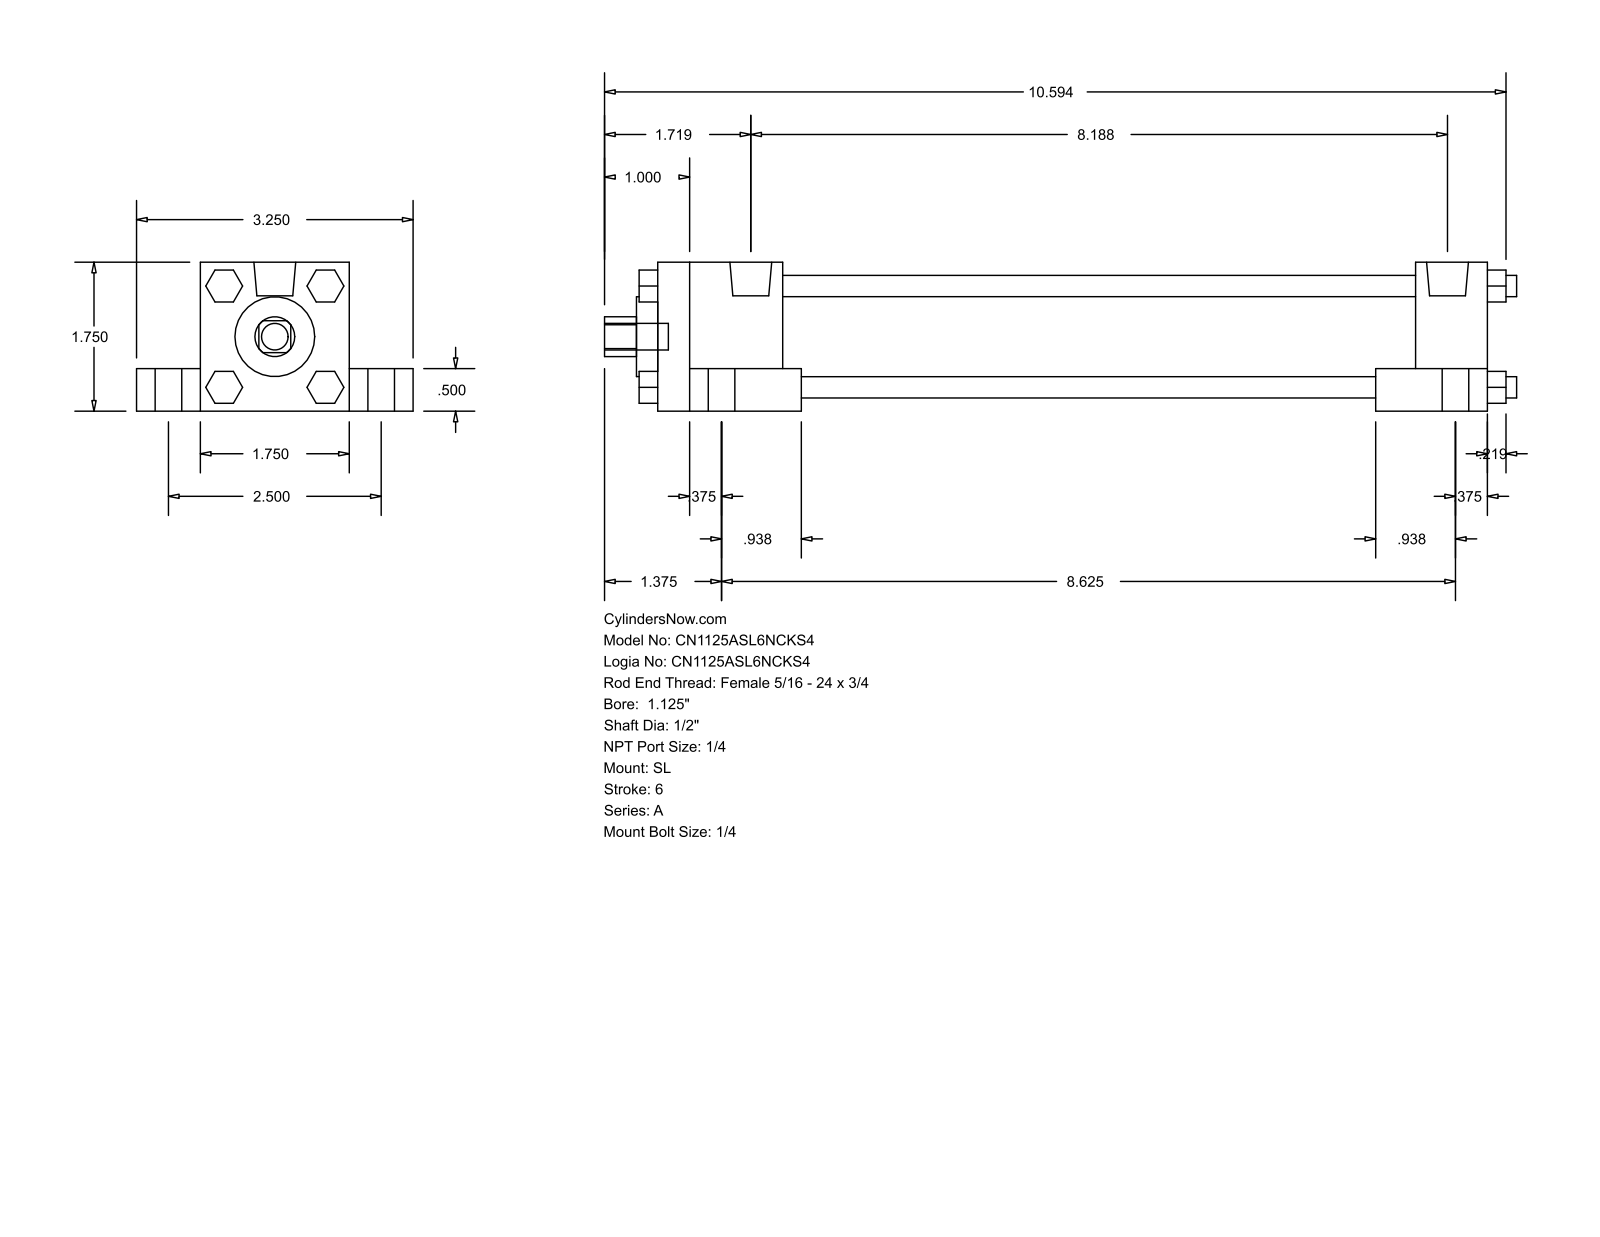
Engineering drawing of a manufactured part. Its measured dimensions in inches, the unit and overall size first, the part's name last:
Units: inches
Overall size (bounding box): 10.719 × 3.25 × 1.75
Round holes (diameter × count): ⌀0.5 ×1, ⌀0.937 ×1, ⌀1.255 ×1
Round bosses / shafts (diameter × count): ⌀0.313 ×5, ⌀0.563 ×4, ⌀0.25 ×4, ⌀0.219 ×4, ⌀0.492 ×2
Partial cylindrical surfaces — rounded edges, fillets, slot ends (radius × count): R0.234 ×1
Main face-to-face distances: 1.75, 1.25, 0.5, 0.75, 2.5, 8.281, 9.75, 8.906, 0.844, 1.469
Bodies: 0 solids, 150 faces (114 planar, 36 cylindrical, 0 other)
Part name (STEP PRODUCT): A_SL__0112_0.5
STEP written by: GSSL Pune (CONFIG_CONTROL_DESIGN)
